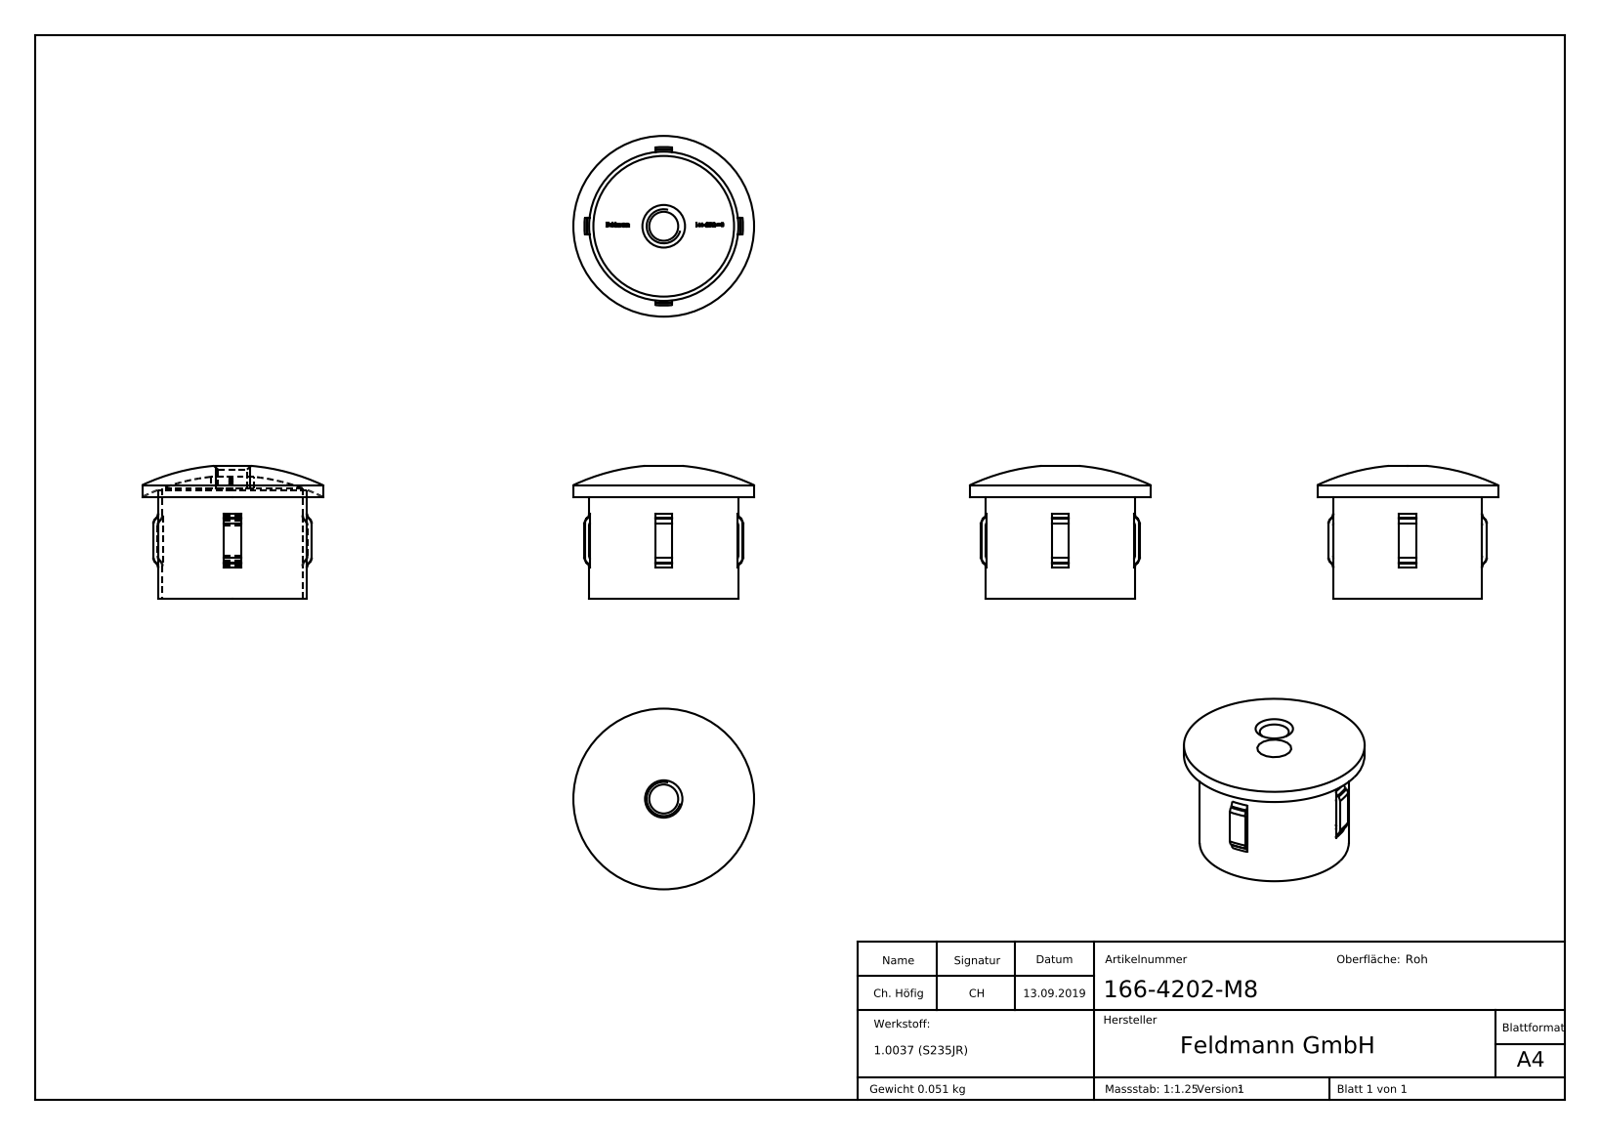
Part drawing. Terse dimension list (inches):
name: 166-4202-M8
written by: SolidWorks 2015 (CONFIG_CONTROL_DESIGN)
unit: in
bodies: 1 solid, 365 faces (130 planar, 20 cylindrical, 215 other)
size: 1.669 × 1.669 × 1.229
volume: 0.397 in³; area: 14.17 in²
holes: 1× ⌀0.268, 1× ⌀1.299
bosses: 1× ⌀1.669, 1× ⌀1.378, 1× ⌀0.394
rounds: 1× R0.693, 1× R0.732
face distances: 0.157, 1.017, 0.079, 0.07, 0.048, 0.033, 0.039, 0.78, 0.089, 0.017
